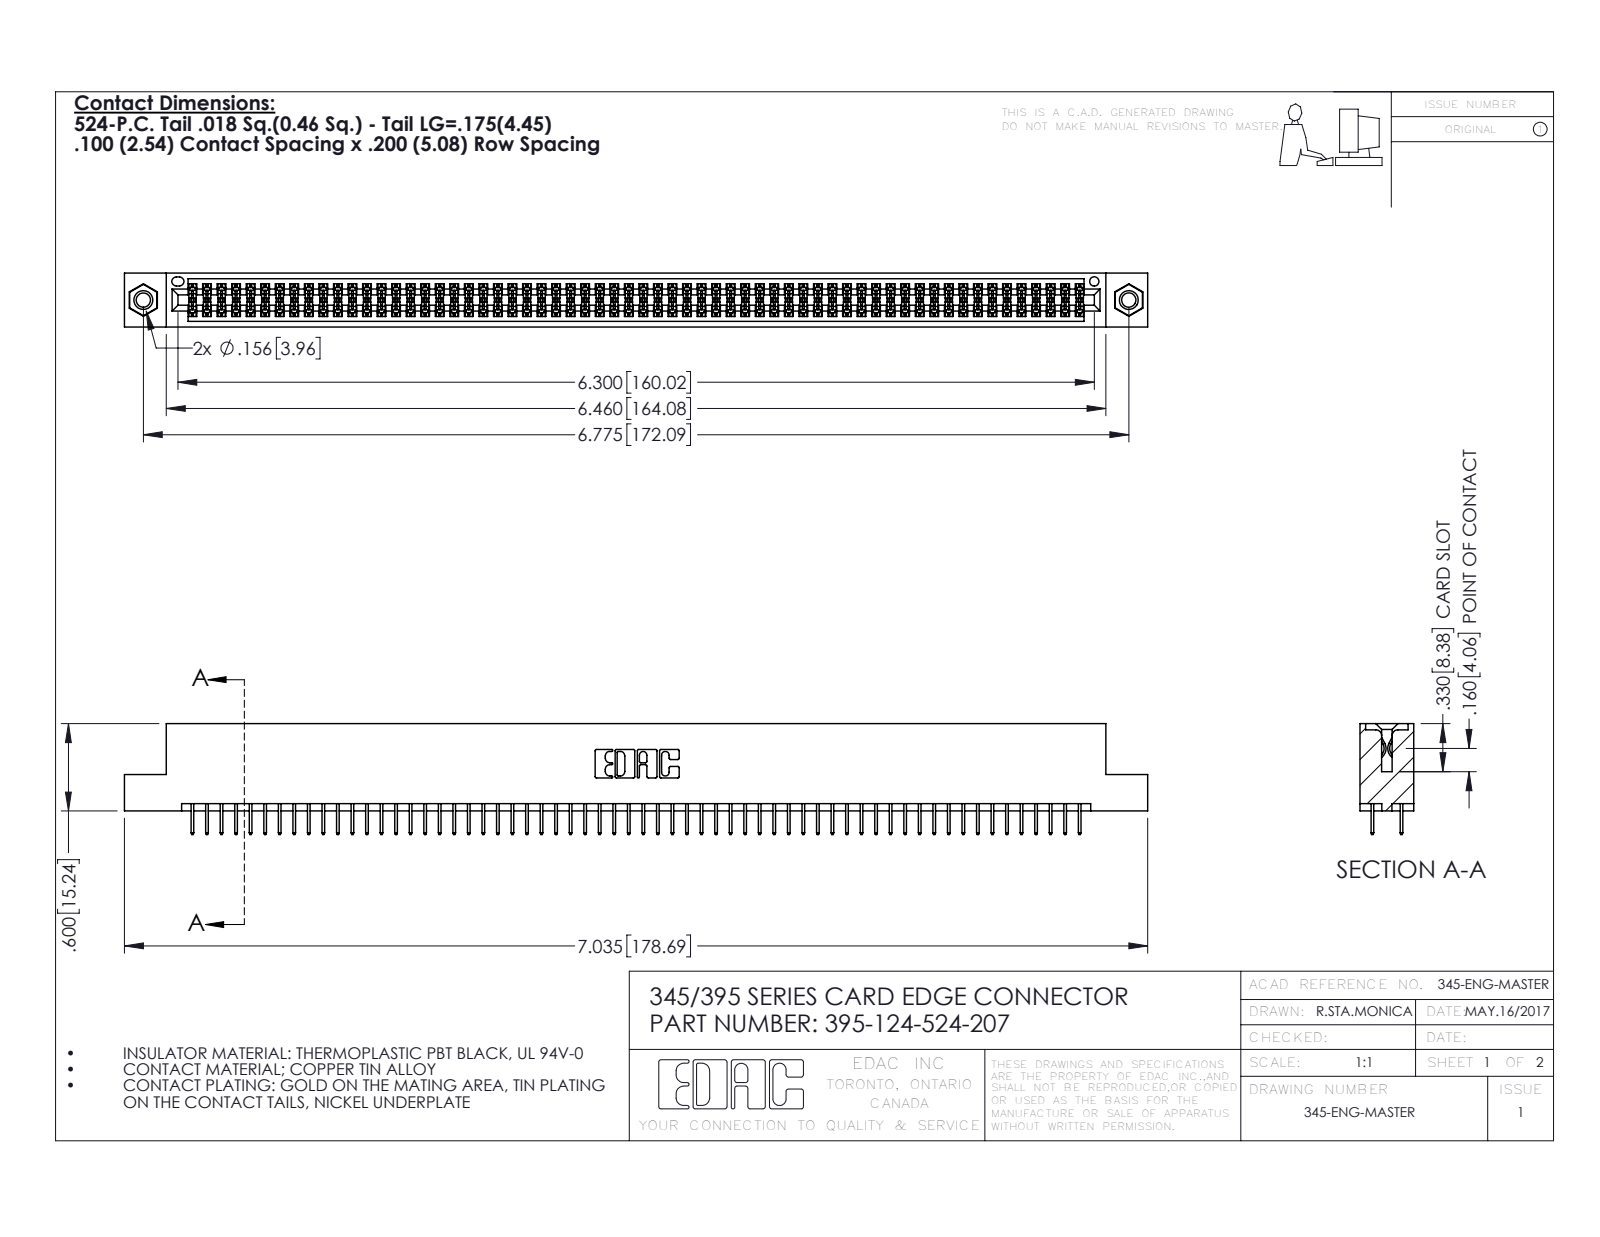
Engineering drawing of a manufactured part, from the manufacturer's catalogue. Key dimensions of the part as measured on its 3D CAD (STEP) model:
Part name (STEP PRODUCT): 395-124-524-207; 345-250-001_345-250-005-103; 345 Part_Flush Mounting Lugs - 0.156 Dia-TI; 345-292-001_345-293-124
STEP written by: SolidWorks 2016 (CONFIG_CONTROL_DESIGN)
Units: inches
Bodies: 127 solids, 6882 faces (4948 planar, 1918 cylindrical, 16 other)
Overall size (bounding box): 7.035 × 0.762 × 0.37
Volume: 1.058 in³ · Surface area: 39.61 in²
Round holes (diameter × count): ⌀0.098 ×2, ⌀0.125 ×2, ⌀0.156 ×2, ⌀0.064 ×1
Round bosses / shafts (diameter × count): ⌀0.155 ×2
Partial cylindrical surfaces — rounded edges, fillets, slot ends (radius × count): R0.006 ×186, R0.01 ×22, R0.007 ×6, R0.031 ×6, R0.026 ×3, R0.014 ×2, R0.019 ×2, R0.022 ×2
Main face-to-face distances: 0.072, 0.298, 0.2, 0.37, 0.098, 0.272, 0.025, 0.225, 0.072, 0.175
Hole centre spacings: 0.27, 6.539, 6.775
